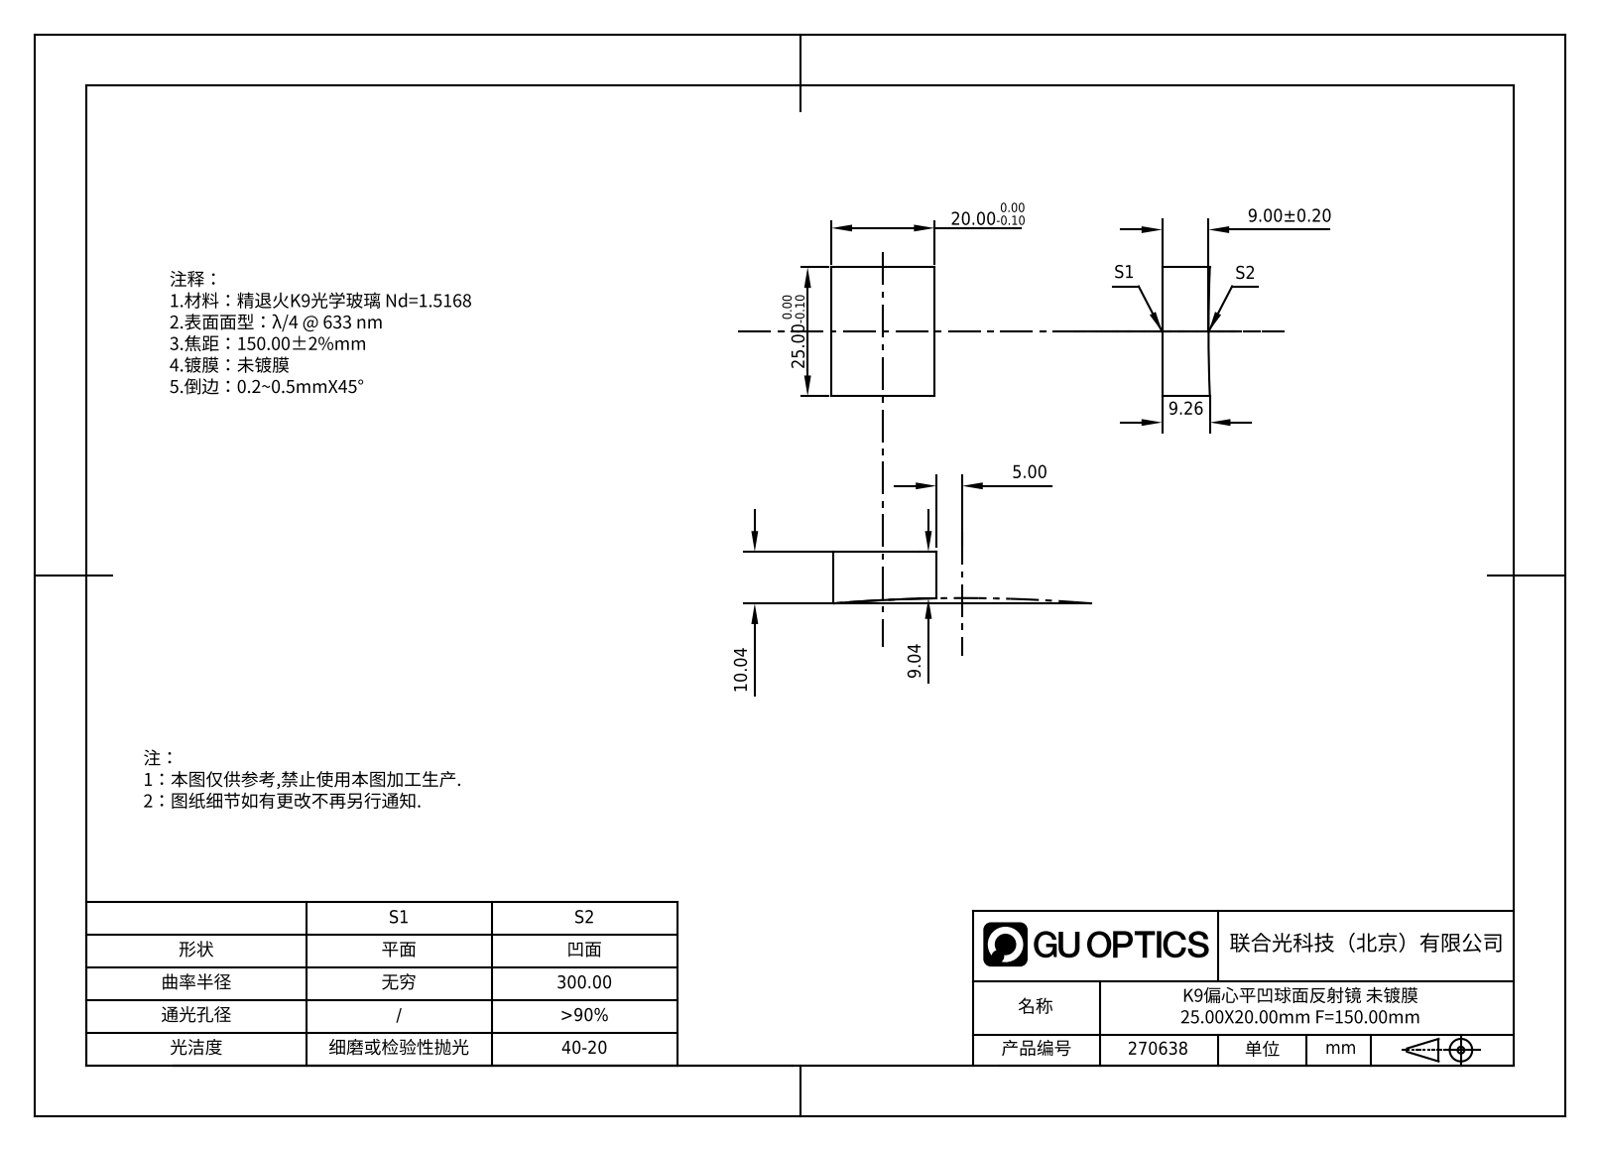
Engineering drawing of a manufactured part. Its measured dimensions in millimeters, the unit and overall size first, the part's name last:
Units: millimetres
Overall size (bounding box): 25 × 20 × 10.3
Main face-to-face distances: 20, 25
Volume: 4 759 mm³ · Surface area: 1 870 mm²
Bodies: 1 solid, 7 faces (5 planar, 0 cylindrical, 2 other)
Part name (STEP PRODUCT): 270638
STEP written by: SolidWorks 2020 (CONFIG_CONTROL_DESIGN)
